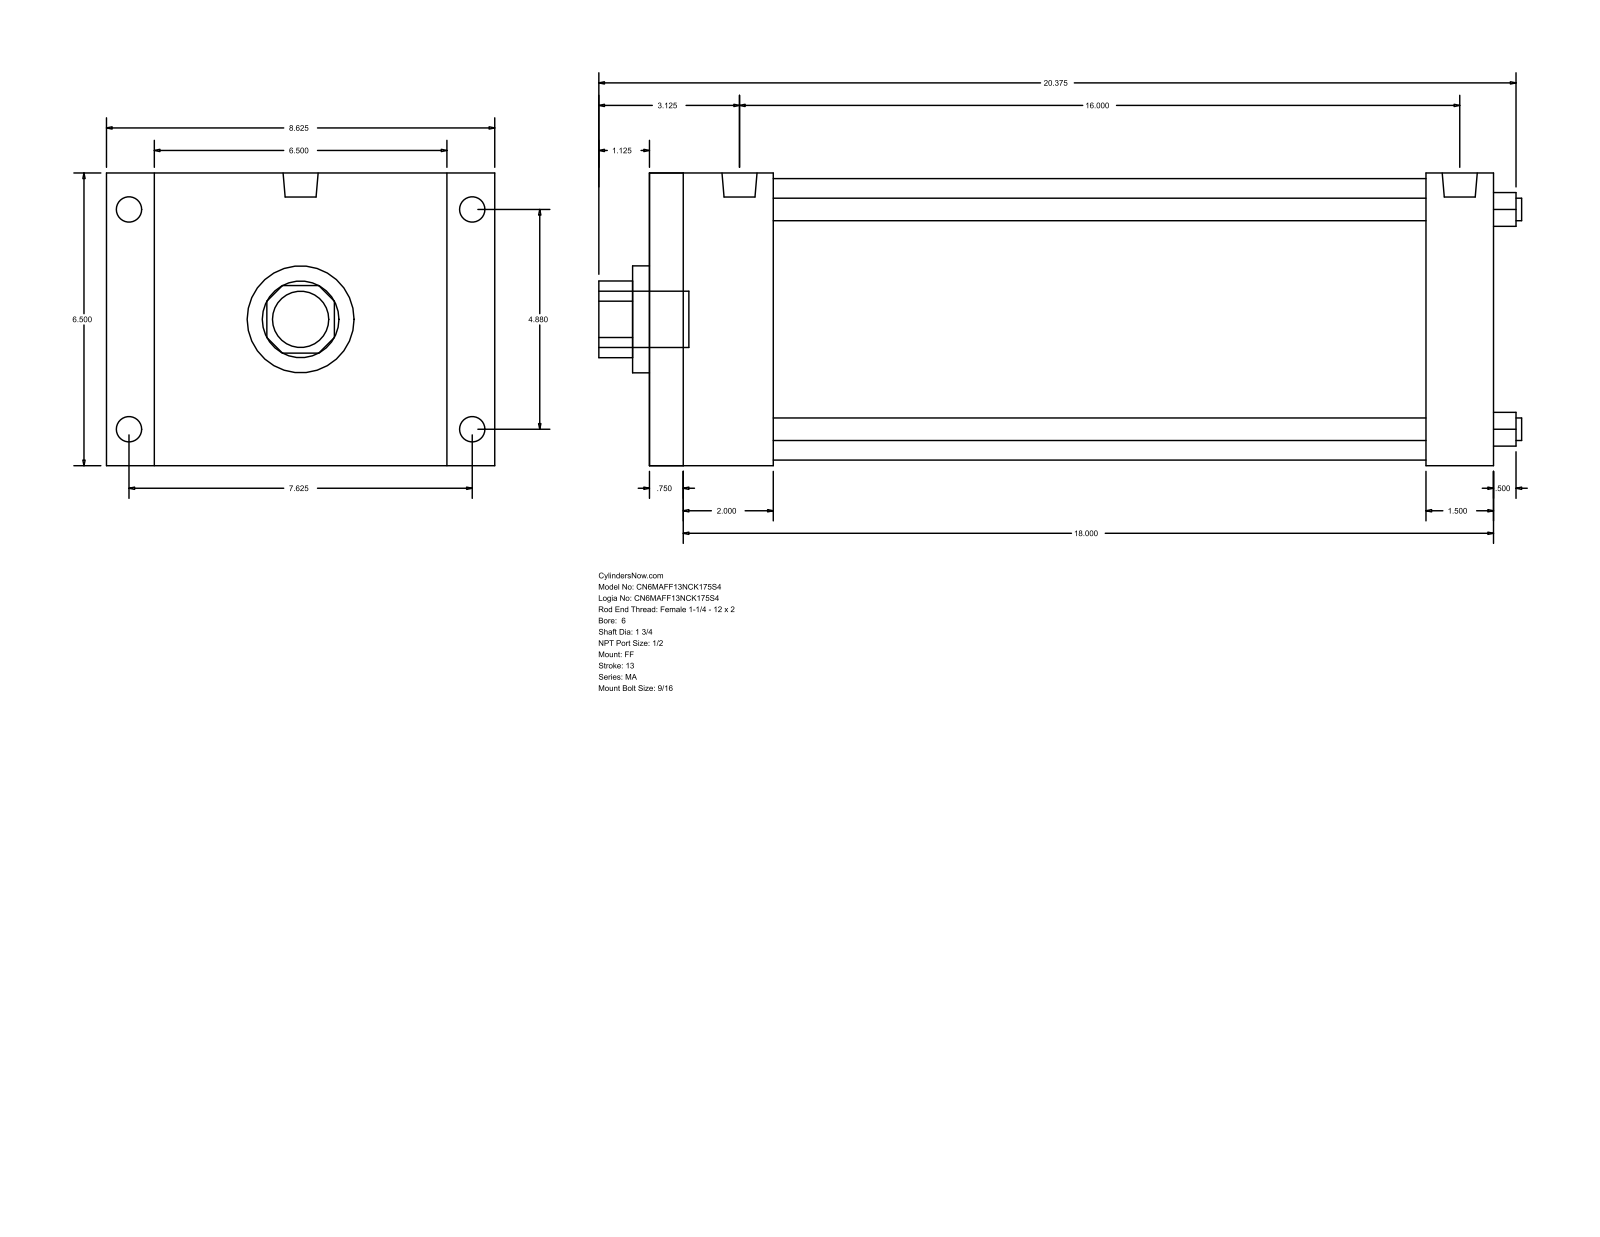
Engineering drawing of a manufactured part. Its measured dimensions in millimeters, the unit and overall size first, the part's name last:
Units: millimetres
Overall size (bounding box): 520.7 × 219.07 × 165.1
Round holes (diameter × count): ⌀12.7 ×4, ⌀44.45 ×1, ⌀60.33 ×1, ⌀158.75 ×1
Round bosses / shafts (diameter × count): ⌀17.46 ×4, ⌀14.29 ×4, ⌀19.77 ×2, ⌀31.75 ×1
Partial cylindrical surfaces — rounded edges, fillets, slot ends (radius × count): R21.63 ×1
Main face-to-face distances: 165.1, 476.25, 19.05, 457.2, 50.8, 69.85, 406.4, 438.16, 419.11, 368.31
Hole centre spacings: 87.65, 123.96, 175.31
Bodies: 0 solids, 92 faces (64 planar, 28 cylindrical, 0 other)
Part name (STEP PRODUCT): MA_FF__0600_1.75
STEP written by: GSSL Pune (CONFIG_CONTROL_DESIGN)
